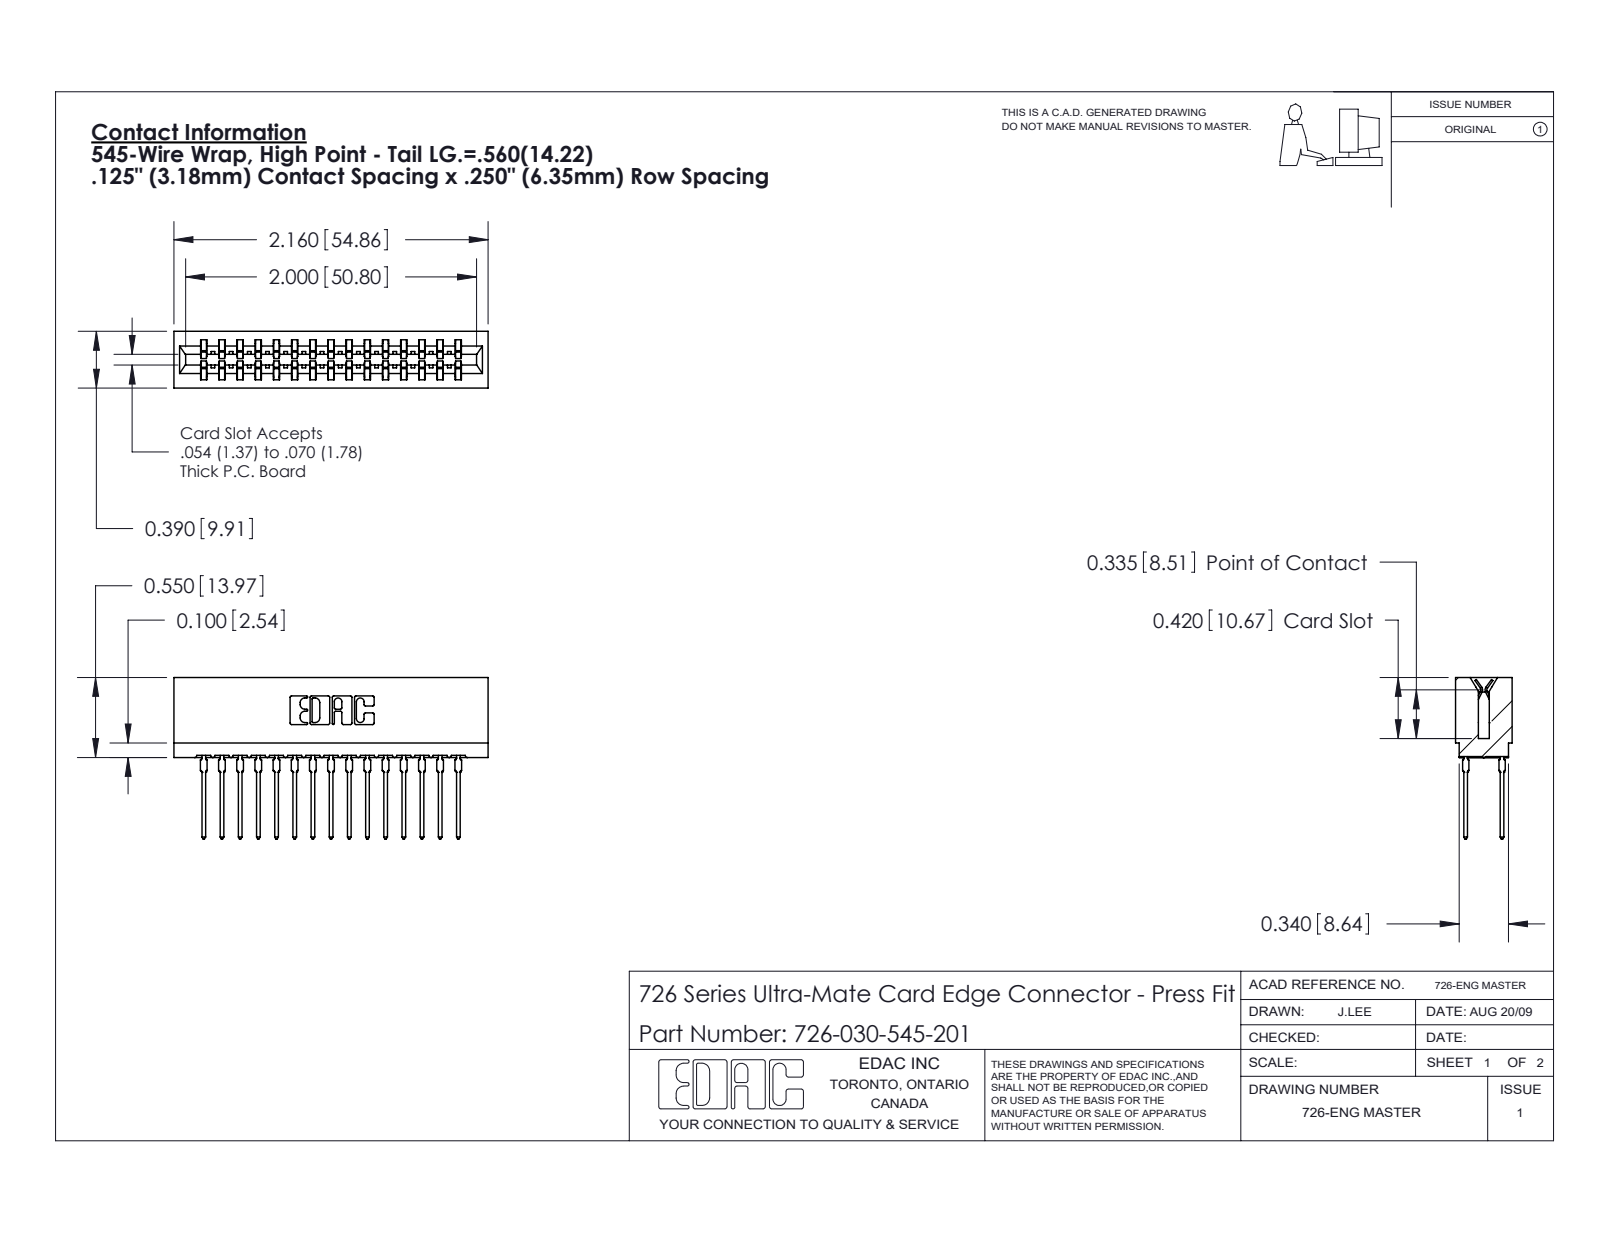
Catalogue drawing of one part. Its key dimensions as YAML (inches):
part_name: "746-292-001_545; 726 Part_.515 Slot Depth - 01; 726-030-545-201"
step_written_by: "SolidWorks 2020 (CONFIG_CONTROL_DESIGN)"
units: inches
bodies: {solids: 31, faces: 2782, planar: 1435, cylindrical: 567, other: 780}
overall_size: [2.16, 1.109, 0.39]
volume: 0.323
surface_area: 13.68
partial_cylinders:
  - {radius: 0.021, count: 60}
  - {radius: 0.01, count: 22}
  - {radius: 0.015, count: 16}
  - {radius: 0.005, count: 8}
  - {radius: 0.011, count: 8}
  - {radius: 0.007, count: 6}
  - {radius: 0.031, count: 6}
  - {radius: 0.026, count: 3}
face_to_face_distances: [0.057, 0.25, 0.333, 0.025, 0.307, 0.083, 0.39, 0.5, 0.75, 0.275]
